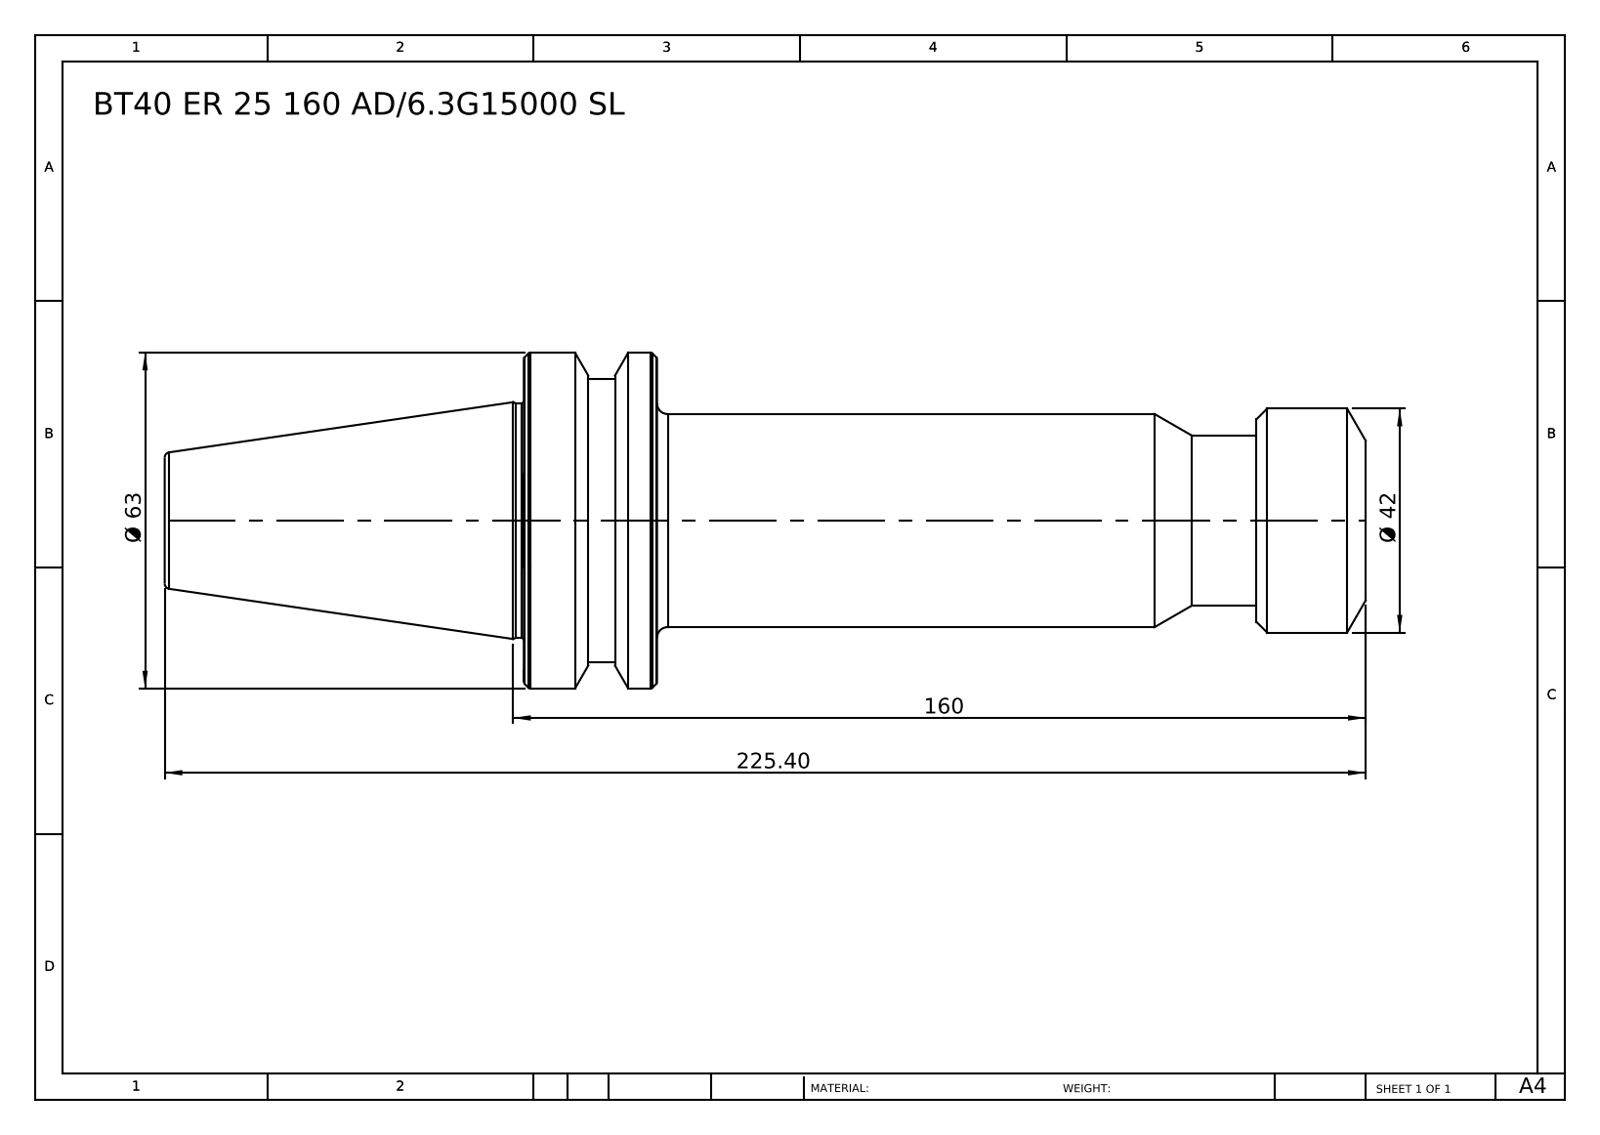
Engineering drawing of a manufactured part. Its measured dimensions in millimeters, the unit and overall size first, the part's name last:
Units: millimetres
Overall size (bounding box): 225.4 × 63 × 63
Round bosses / shafts (diameter × count): ⌀63 ×1, ⌀53 ×1, ⌀44 ×1, ⌀42 ×1, ⌀40 ×1, ⌀31.9 ×1
Main face-to-face distances: 25, 133, 158, 225.4, 92.4, 67.4, 20.5, 112.5, 137.5, 204.9
Volume: 299 573 mm³ · Surface area: 34 989 mm²
Bodies: 1 solid, 62 faces (7 planar, 14 cylindrical, 41 other)
Part name (STEP PRODUCT): BT40 ER 25 160 AD-6.3G15000 SL
STEP written by: SolidWorks 2014 (CONFIG_CONTROL_DESIGN)
